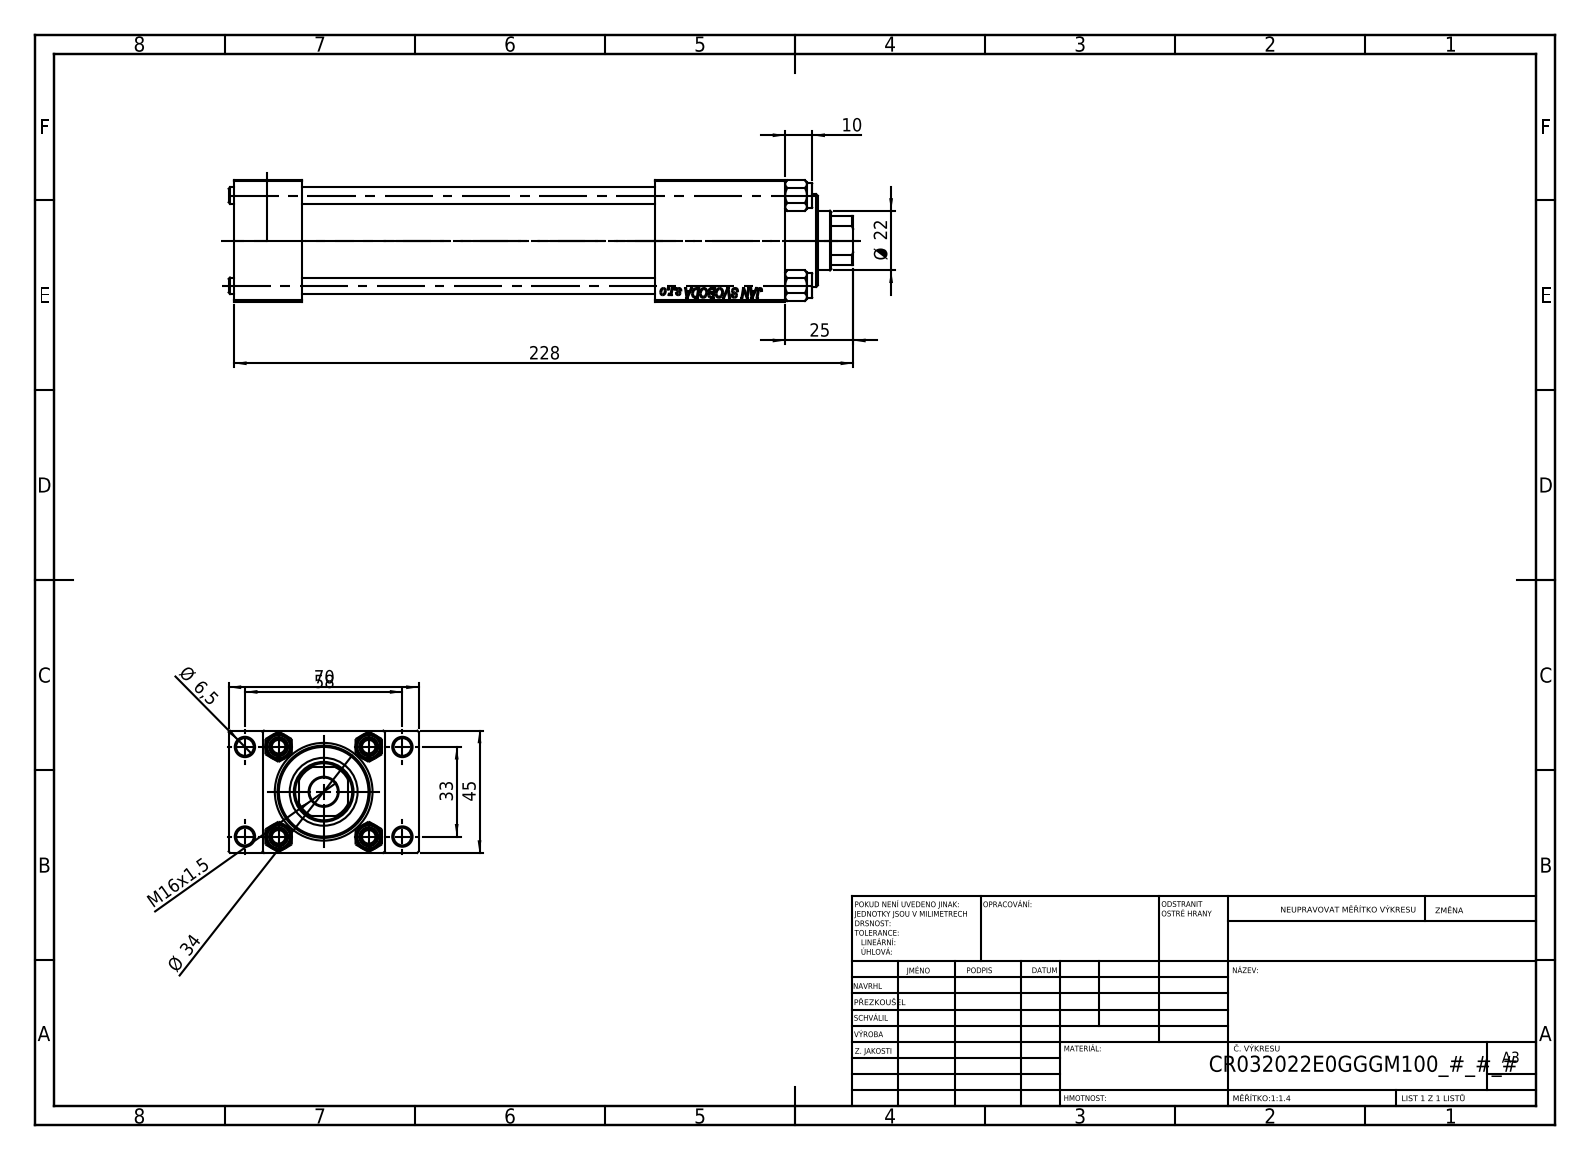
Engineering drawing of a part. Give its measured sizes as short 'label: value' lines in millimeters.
name: V215CR_VCP_E; NUT_M5_E; V215_VC_A; V215CR_E_Body (+1 more)
written by: SolidWorks 2019 (CONFIG_CONTROL_DESIGN)
unit: mm
bodies: 11 solids, 1136 faces (497 planar, 87 cylindrical, 552 other)
size: 230 × 70 × 45
volume: 302 336 mm³; area: 109 746 mm²
holes: 4× ⌀6, 4× ⌀6.5, 2× ⌀7, 2× ⌀13.16, 2× ⌀20, 1× ⌀10.5, 1× ⌀22, 1× ⌀24, 1× ⌀25, 1× ⌀32, 1× ⌀33
bosses: 4× ⌀9, 1× ⌀38, 1× ⌀34
rounds: 1× R10.5
face distances: 45, 25, 12.5, 57.5, 203, 70, 155, 130, 178, 48
hole spacings: 12.4, 23.48, 33.2, 33.37, 35.35, 45.6, 56.35, 33
